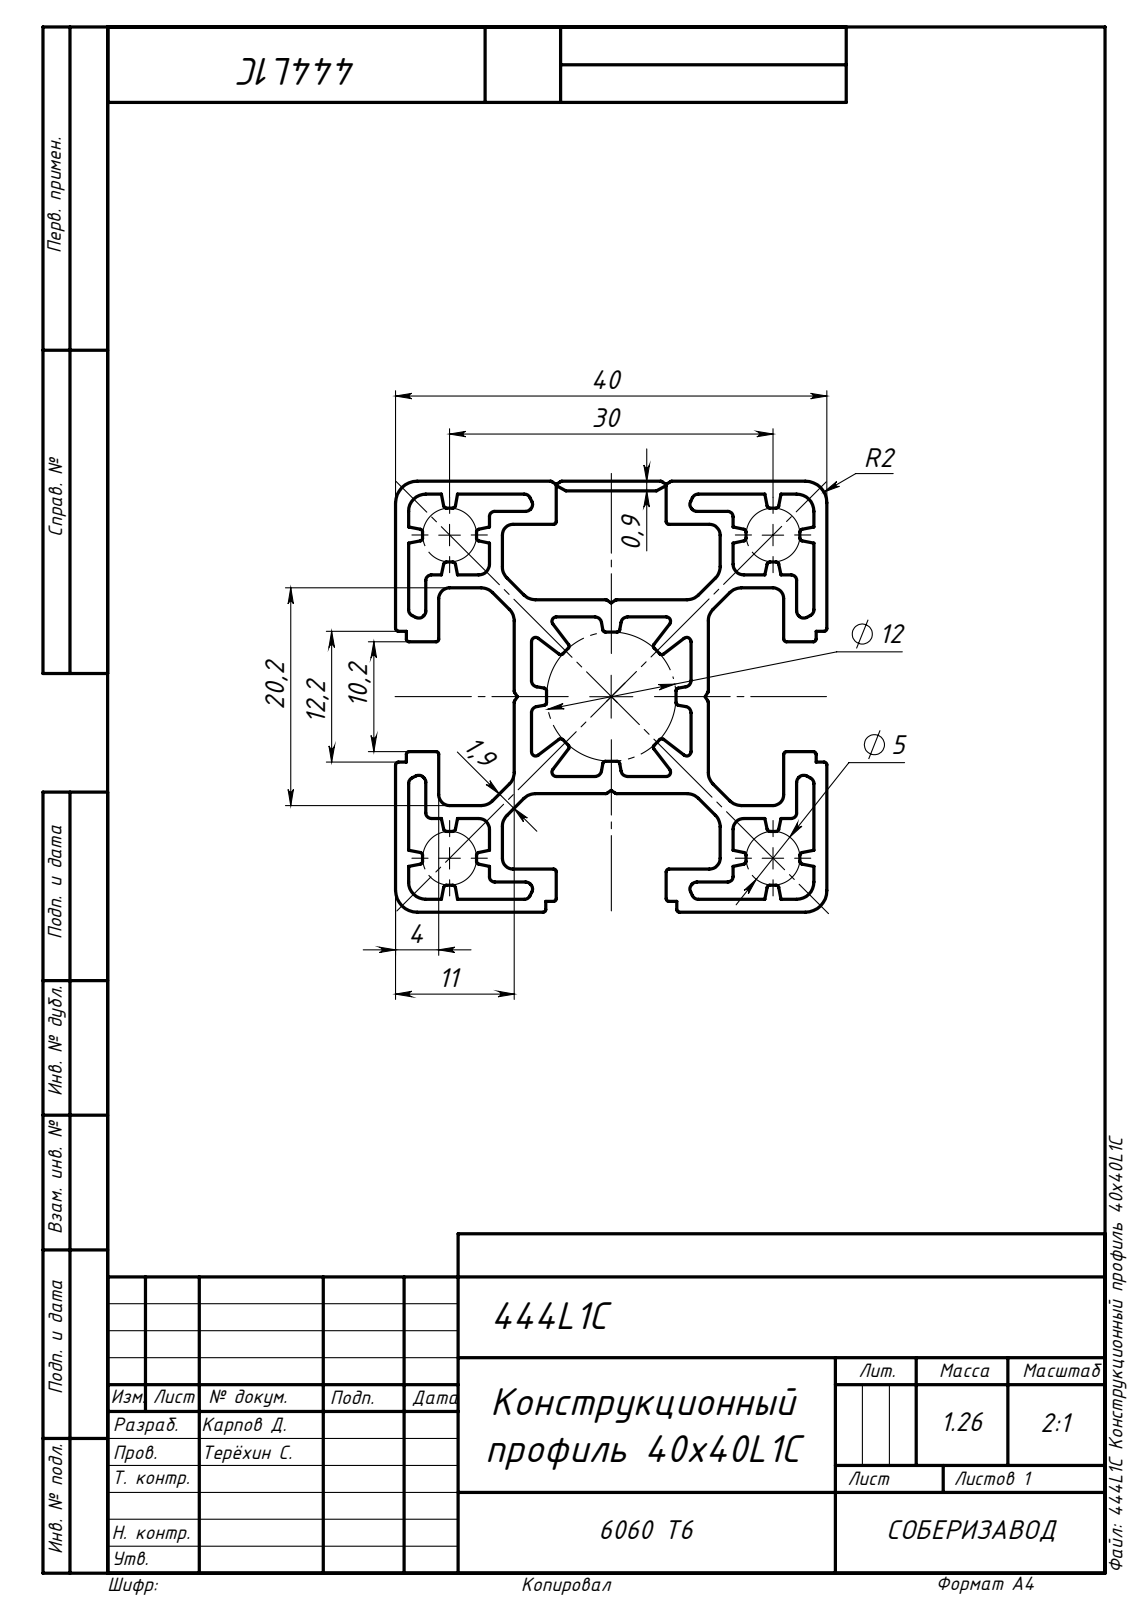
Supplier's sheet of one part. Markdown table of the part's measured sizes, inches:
| quantity | value |
| --- | --- |
| STEP written by | SolidWorks 2014 (AUTOMOTIVE_DESIGN) |
| units | inches |
| bodies | 1 solid, 402 faces (214 planar, 188 cylindrical, 0 other) |
| overall size | 39.37 × 1.575 × 1.575 |
| volume | 28.59 in³ |
| surface area | 948.8 in² |
| partial cylindrical surfaces (radius × count) | 0.01 × 80, 0.024 × 32, 0.059 × 16, 0.039 × 12, 0.016 × 8, 0.02 × 8, 0.063 × 4, 0.079 × 4 |
| main face-to-face distances | 0.047, 0.386, 1.528, 0.11, 1.417, 0.433, 1.142, 1.094, 1.031, 0.063 |
